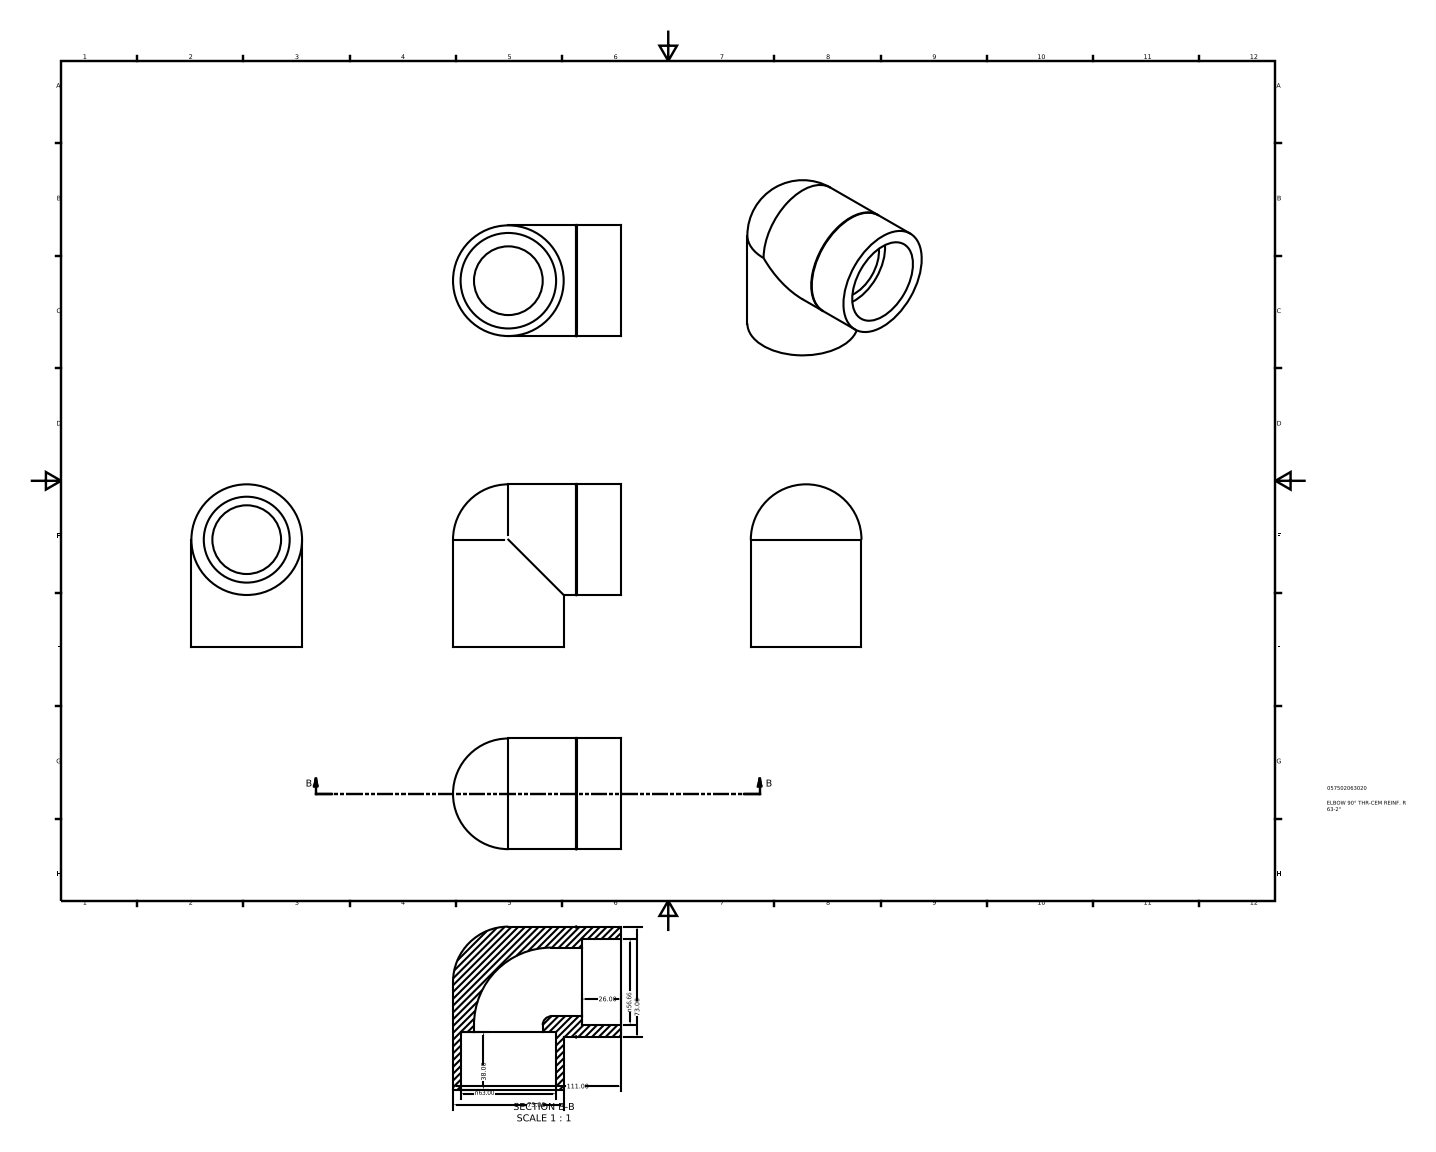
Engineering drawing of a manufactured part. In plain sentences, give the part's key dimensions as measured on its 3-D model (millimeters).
The part is named "057502063020". Its 3-D file was written by "Autodesk Inventor 2015 (AUTOMOTIVE_DESIGN)". It is 1 solid with 15 faces: 4 planar, 7 cylindrical and 4 other. Overall it measures 111 by 107.5 by 73 millimeters. Its volume is 299 148 cubic millimeters and its surface area 59 531 square millimeters. Round holes: 2 of diameter 45.32, 1 of diameter 56.66, 1 of diameter 63. Round bosses or shafts: 2 of diameter 73. The main face-to-face distances are 38, 26.
